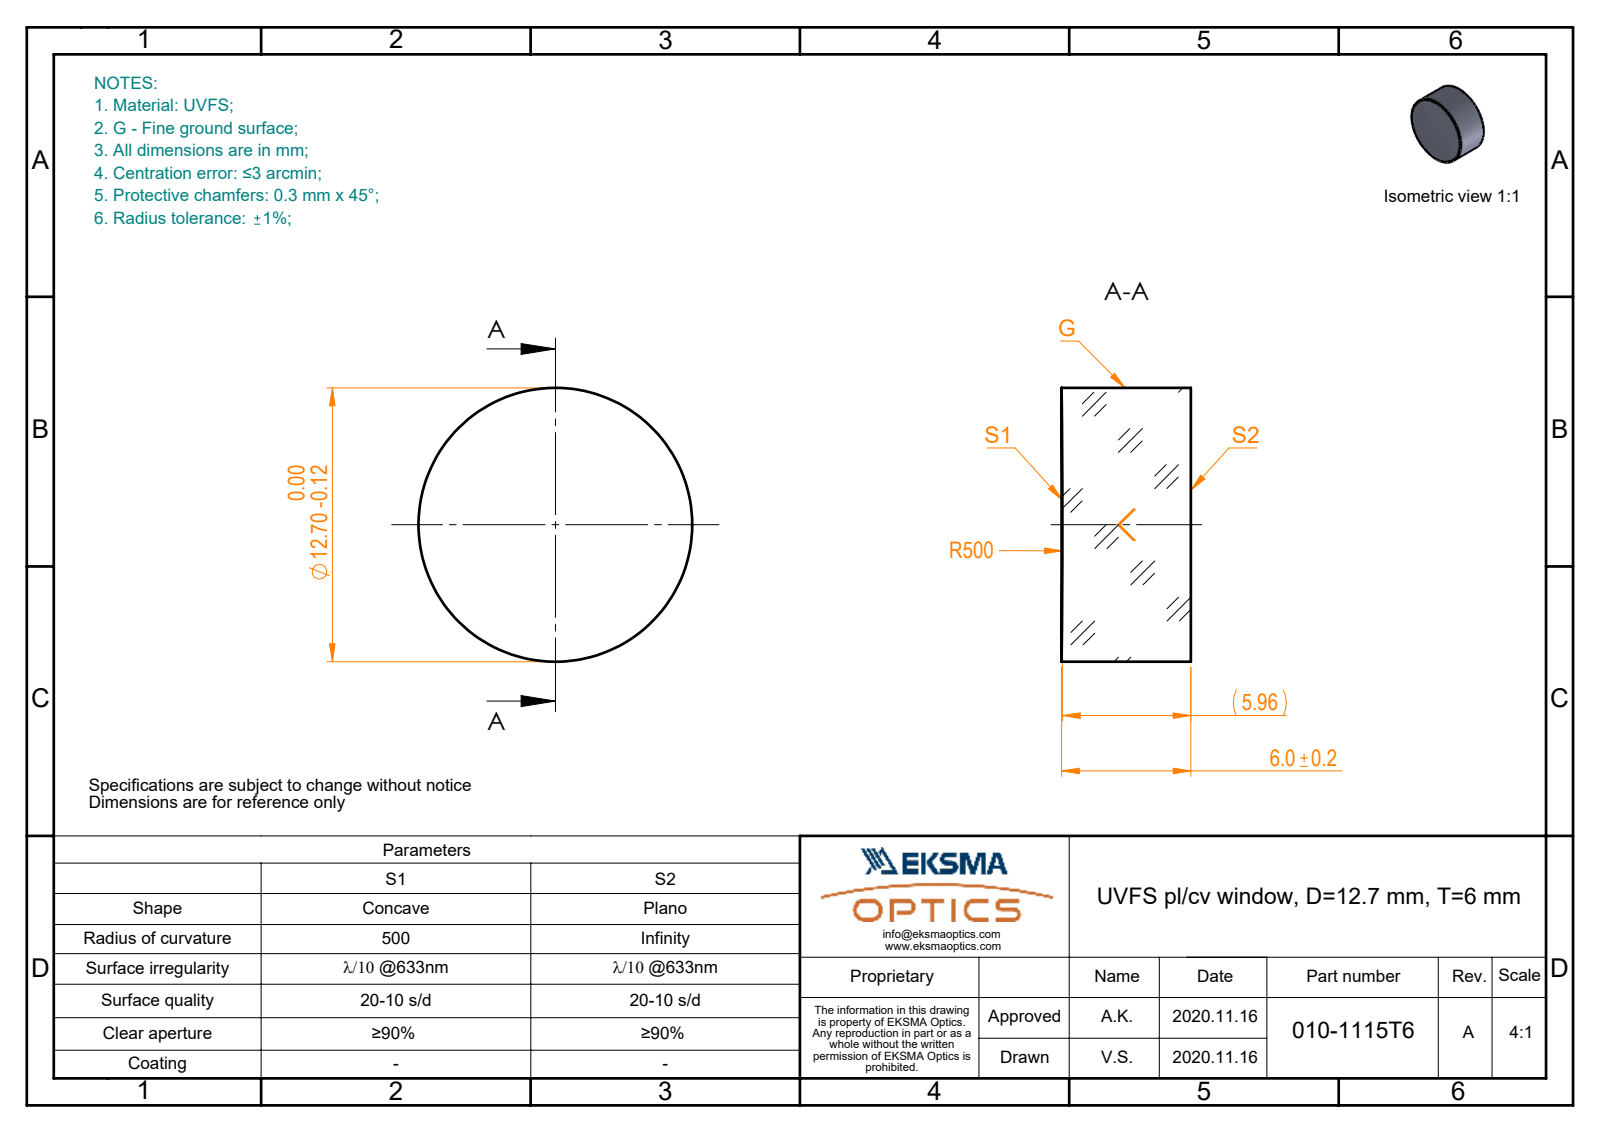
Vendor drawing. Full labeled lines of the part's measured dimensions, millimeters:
Part name (STEP PRODUCT): 010-1115T6_UVFS_PCV_window
STEP written by: SolidWorks 2019 (CONFIG_CONTROL_DESIGN)
Units: millimetres
Bodies: 1 solid, 5 faces (1 planar, 2 cylindrical, 2 other)
Overall size (bounding box): 12.7 × 12.7 × 6
Volume: 758 mm³ · Surface area: 493 mm²
Round bosses / shafts (diameter × count): ⌀12.7 ×1
